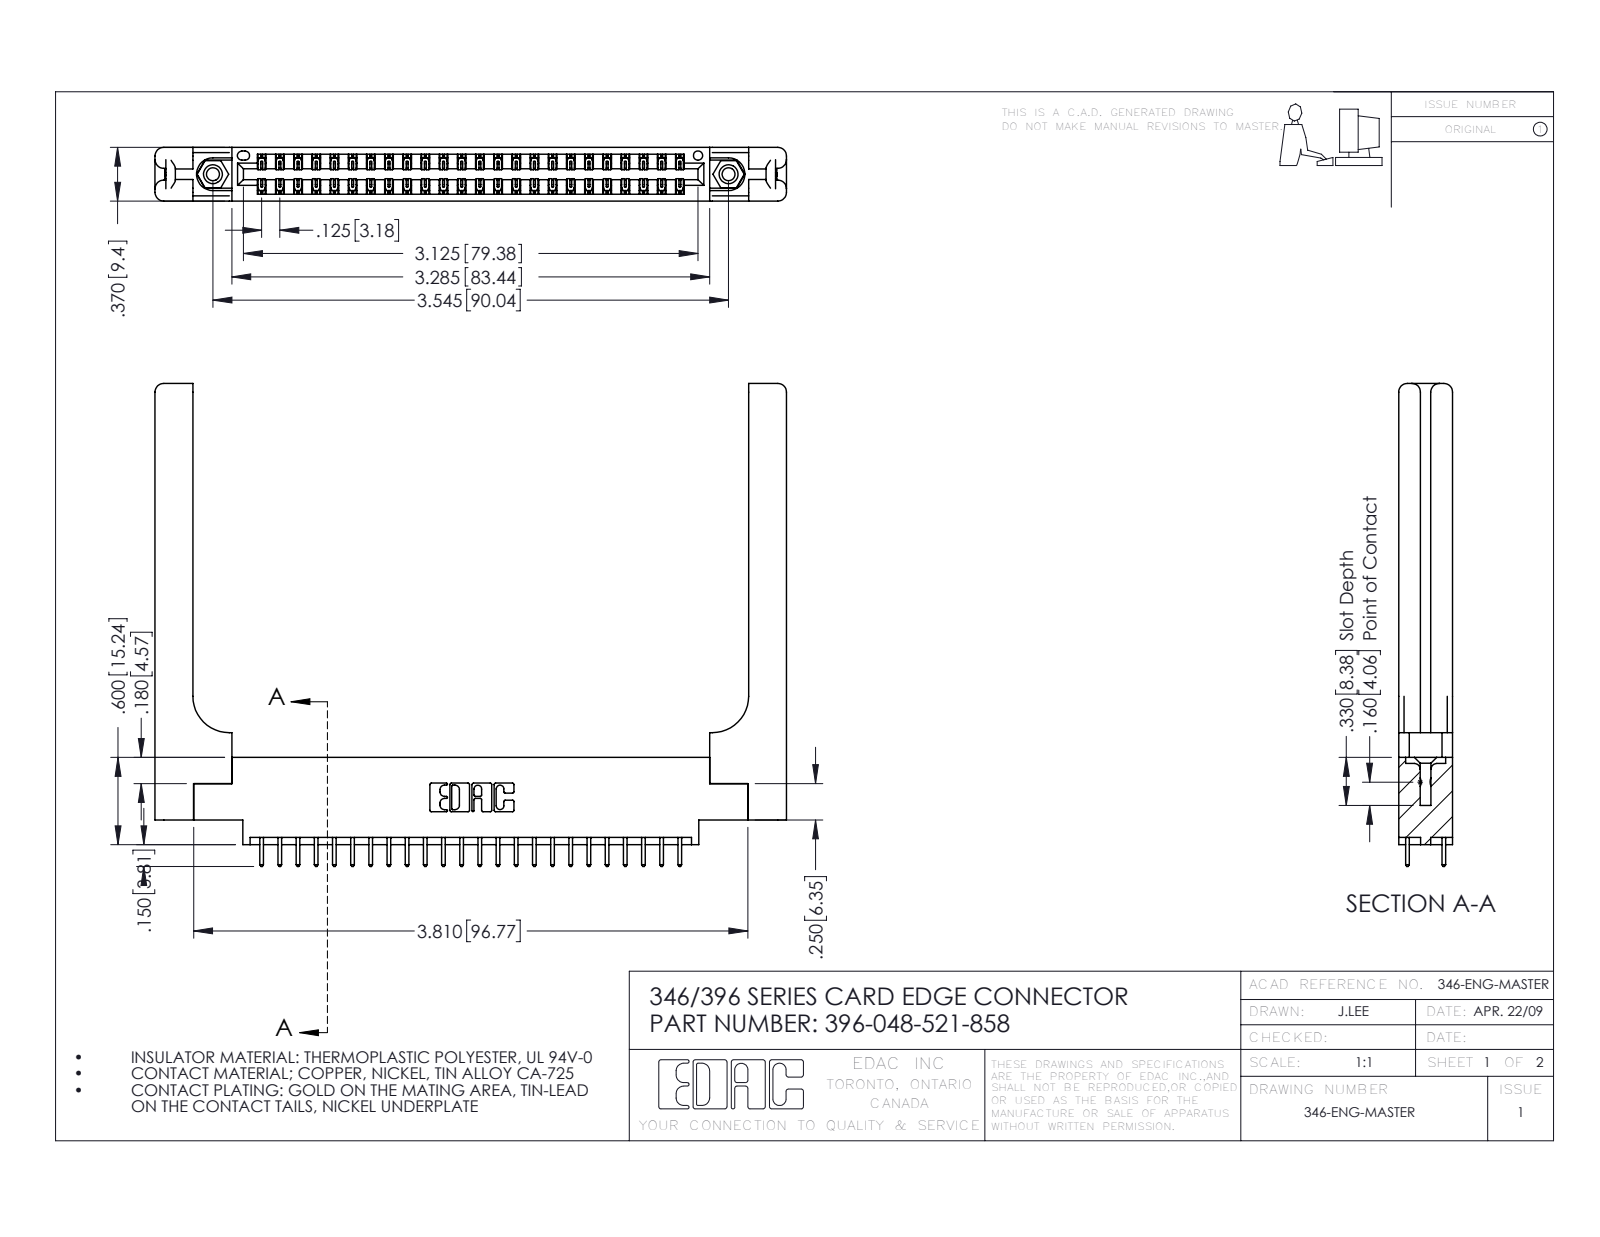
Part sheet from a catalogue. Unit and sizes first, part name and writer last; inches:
Units: inches
Overall size (bounding box): 4.341 × 3.32 × 0.37
Round holes (diameter × count): ⌀0.089 ×2, ⌀0.125 ×2, ⌀0.156 ×2, ⌀0.064 ×1
Round bosses / shafts (diameter × count): ⌀0.155 ×2
Partial cylindrical surfaces — rounded edges, fillets, slot ends (radius × count): R0.006 ×72, R0.01 ×48, R0.01 ×22, R0.06 ×16, R0.007 ×6, R0.031 ×6, R0.026 ×3, R0.014 ×2
Main face-to-face distances: 0.37, 0.072, 0.048, 0.322, 0.148, 0.15, 0.25, 0.025, 0.298, 0.275
Hole centre spacings: 0.246, 3.337, 3.545
Volume: 1.094 in³ · Surface area: 29.58 in²
Bodies: 53 solids, 2878 faces (1908 planar, 910 cylindrical, 60 other)
Part name (STEP PRODUCT): 396-048-521-858; 345-292-001_345-293-121; 345-250-001_345-250-001-102; 346-220-058_345-220-058 (+1 more)
STEP written by: SolidWorks 2016 (CONFIG_CONTROL_DESIGN)
